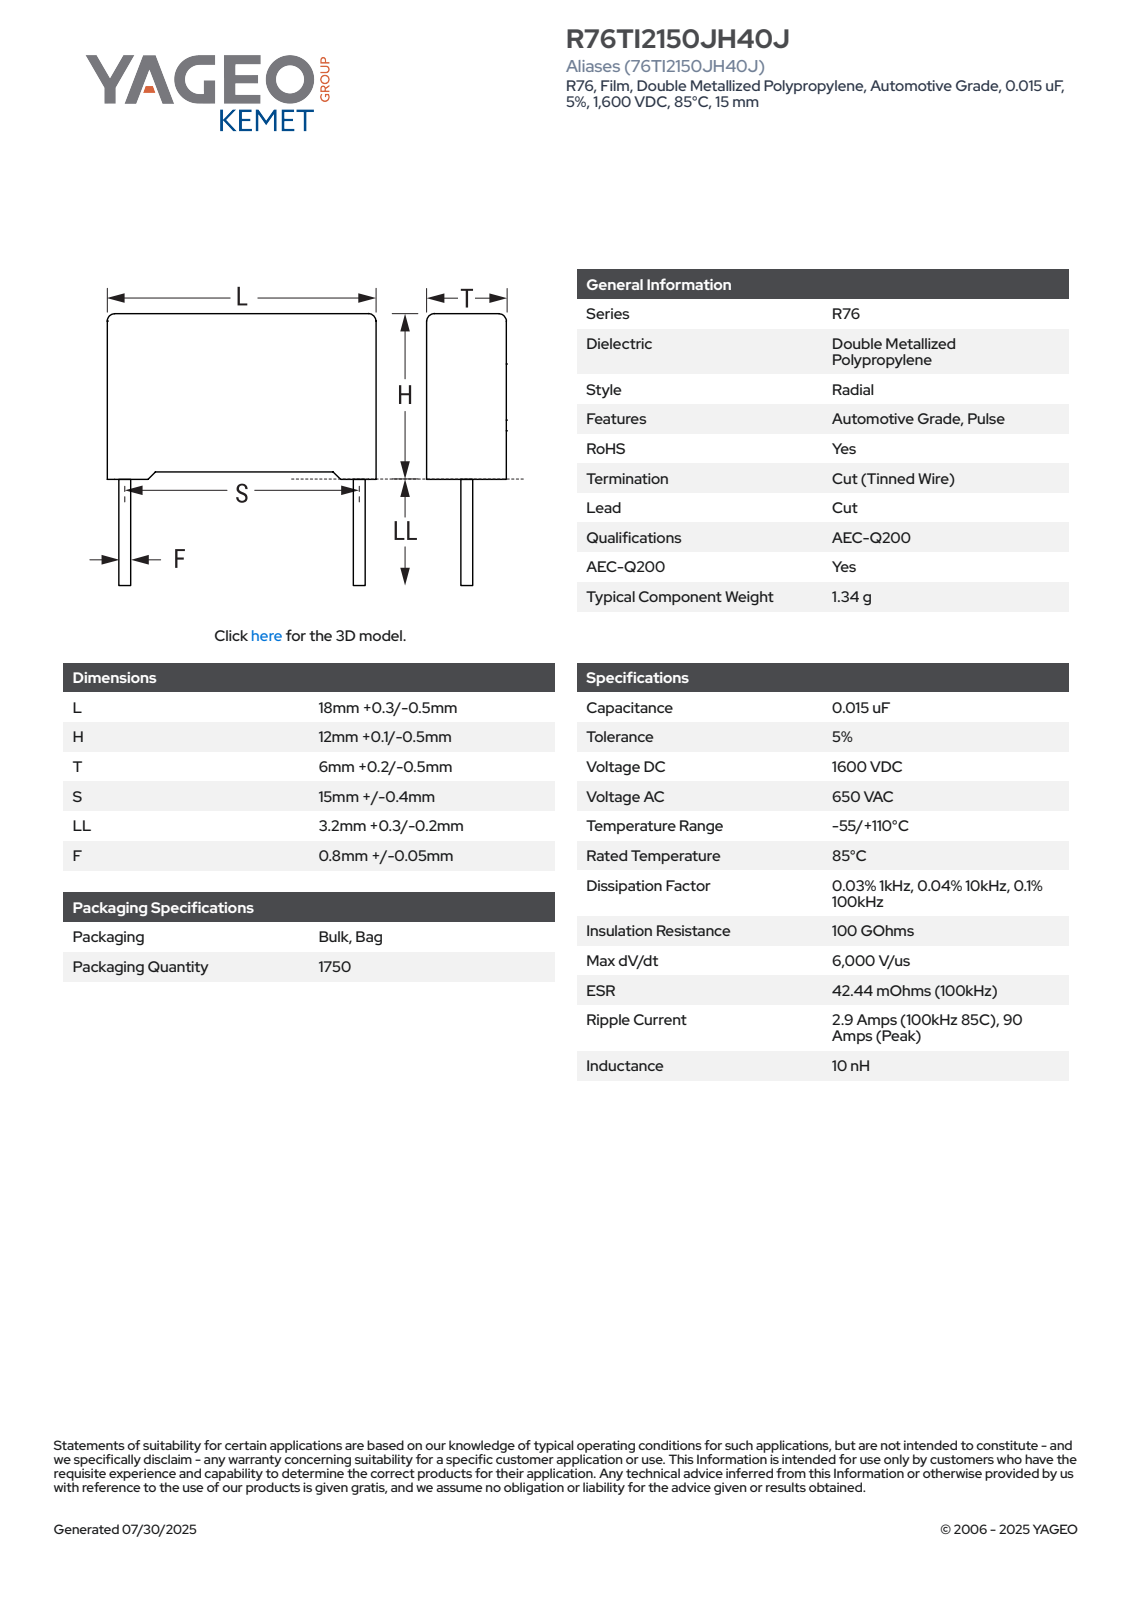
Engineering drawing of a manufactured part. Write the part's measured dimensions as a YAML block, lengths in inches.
part_name: "CFR_RB2_18X12X6_L18.3H12.1T6.2S15LL3.5F0.85"
step_written_by: "SolidWorks 2021 (AUTOMOTIVE_DESIGN)"
units: inches
bodies: {solids: 4, faces: 85, planar: 77, cylindrical: 8, other: 0}
overall_size: [0.72, 0.614, 0.244]
volume: 0.08
surface_area: 1.35
round_bosses_or_shafts:
  - {diameter: 0.033, count: 2}
partial_cylinders:
  - {radius: 0.02, count: 4}
face_to_face_distances: [0.244, 0.447, 0.72, 0.024, 0.22, 0.03, 0.476, 0.017, 0.013, 0.46]
